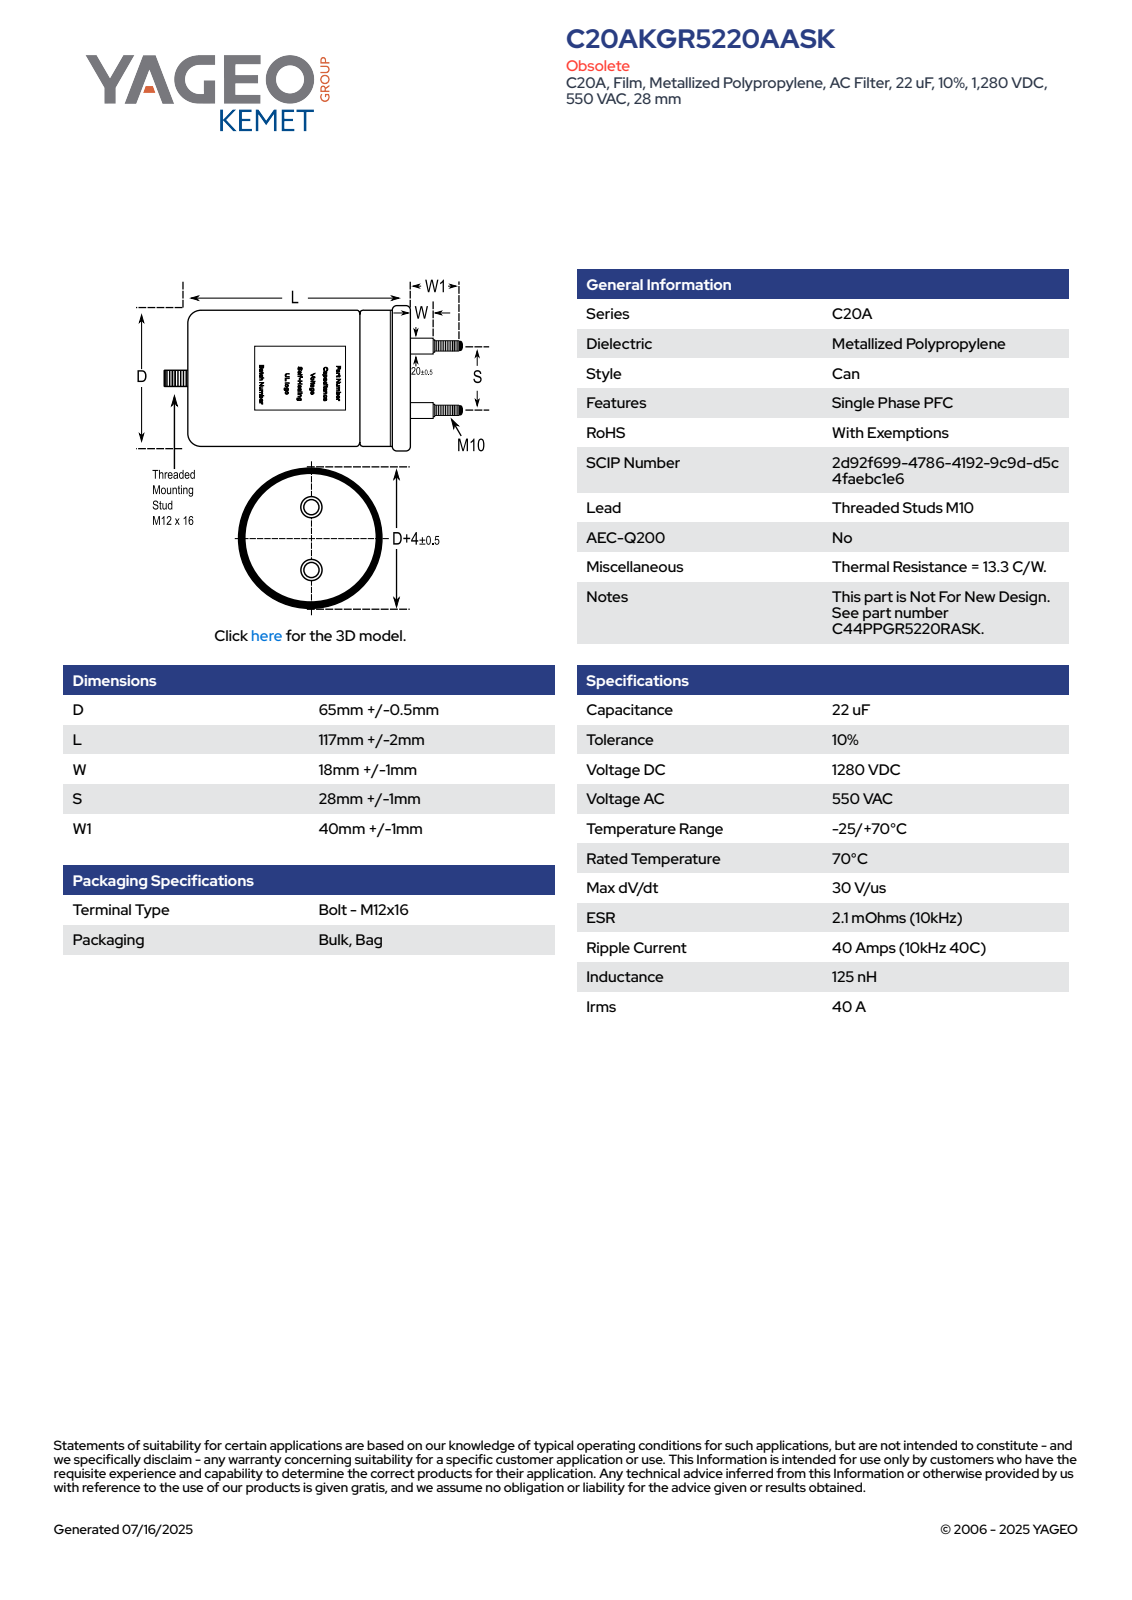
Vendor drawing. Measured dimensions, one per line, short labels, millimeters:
name: CFP_C44P_65X117_D65.5L119S28
written by: SolidWorks 2014 (AUTOMOTIVE_DESIGN)
unit: mm
bodies: 1 solid, 105 faces (32 planar, 36 cylindrical, 37 other)
size: 176 × 70 × 70
volume: 419 023 mm³; area: 35 978 mm²
bosses: 3× ⌀12, 2× ⌀20.5, 2× ⌀10, 1× ⌀70, 1× ⌀65.5
rounds: 1× R32.76
face distances: 119, 137, 18, 115.18, 3.82, 21.82, 160, 44.82, 41, 23
